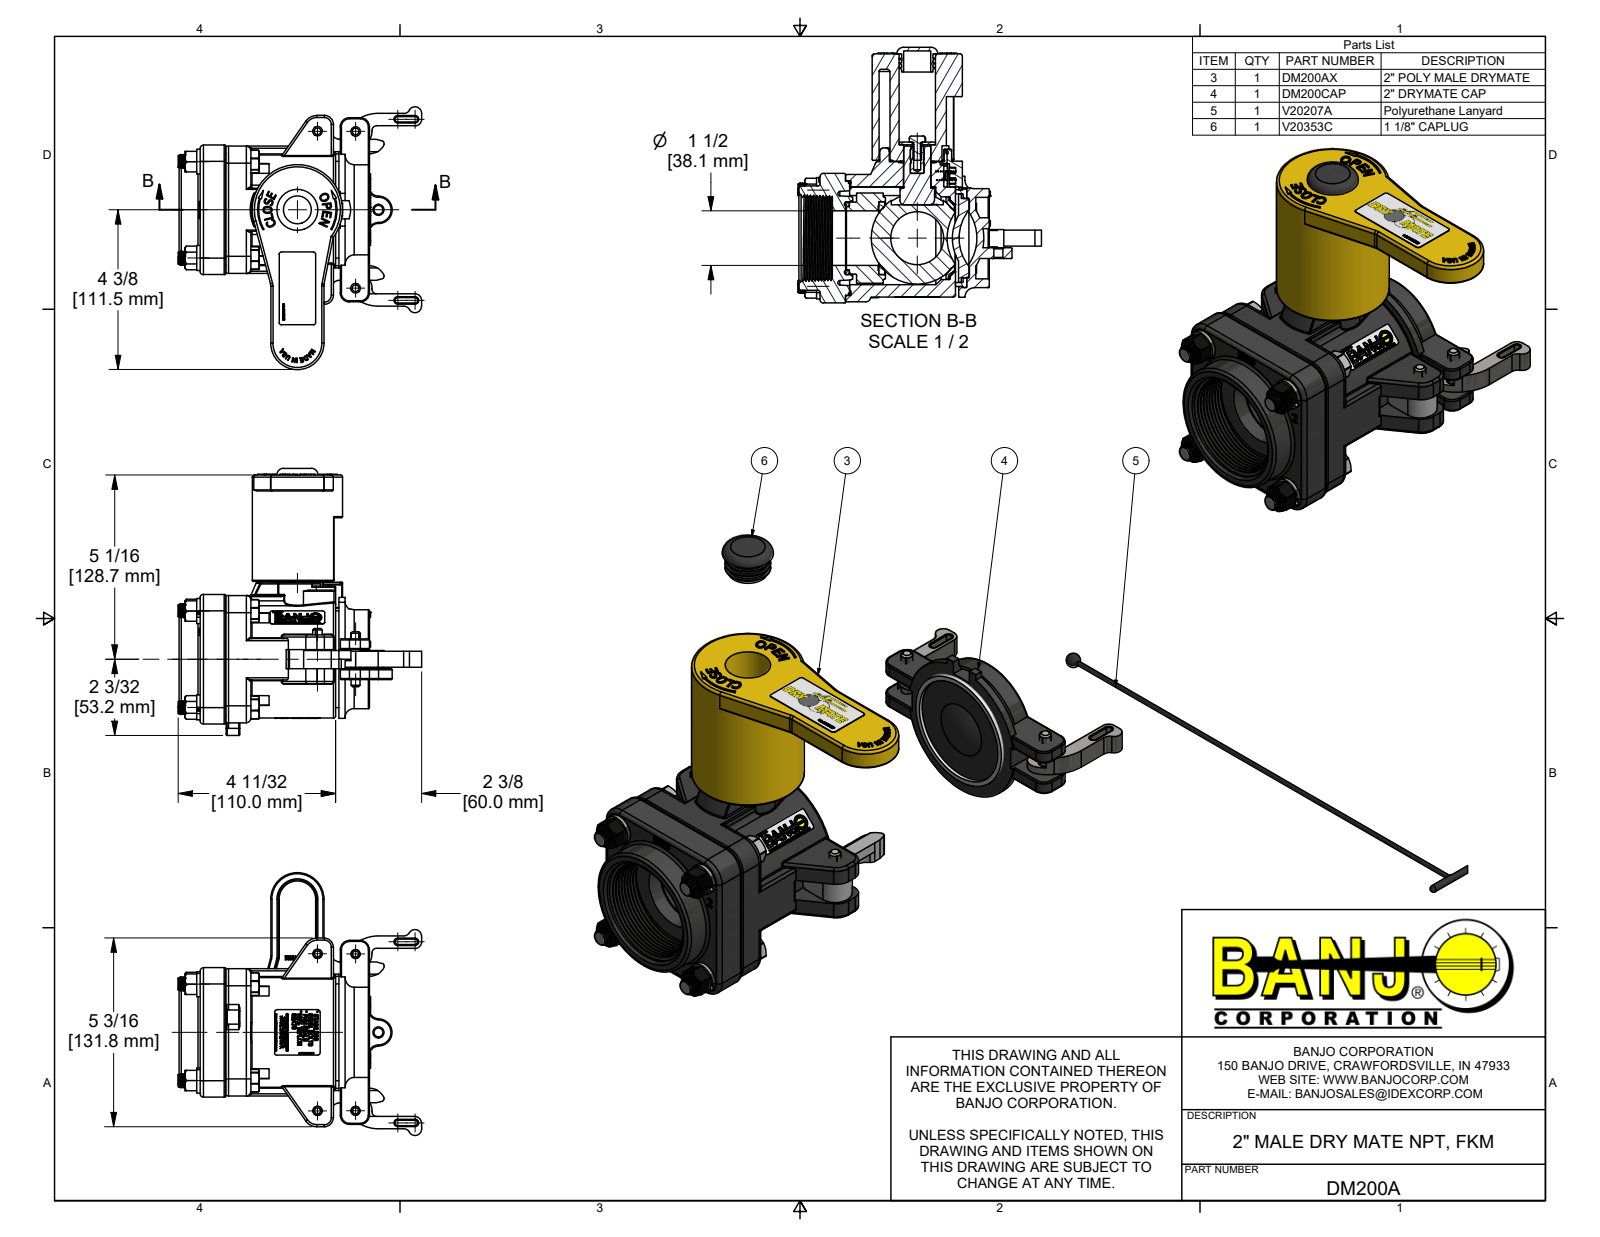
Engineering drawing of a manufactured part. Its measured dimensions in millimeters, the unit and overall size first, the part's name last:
Units: millimetres
Overall size (bounding box): 186.4 × 183.4 × 170.1
Round holes (diameter × count): ⌀6.4 ×5, ⌀9.5 ×5, ⌀6.5 ×4, ⌀7.8 ×4, ⌀9.8 ×4, ⌀10.3 ×4, ⌀10.7 ×4, ⌀3.2 ×3, ⌀5 ×1, ⌀5.1 ×1, ⌀5.8 ×1, ⌀7.1 ×1
Round bosses / shafts (diameter × count): ⌀8.2 ×60, ⌀17.4 ×4, ⌀9.5 ×4, ⌀6.6 ×4, ⌀6.3 ×4, ⌀7.1 ×3, ⌀63 ×2, ⌀82.6 ×1
Partial cylindrical surfaces — rounded edges, fillets, slot ends (radius × count): R0.8 ×104, R1.5 ×52, R0.5 ×20, R0.3 ×12, R3.2 ×10, R6.4 ×10, R2.3 ×8, R4.1 ×8
Main face-to-face distances: 7.6, 94.6, 7.5, 0.8, 89.7, 6.4, 20.9, 20.9, 17.8, 76.8
Hole centre spacings: 67.4, 47.5, 47.8, 67.3, 67.5, 95.3, 24.1, 25
Volume: 816 400 mm³ · Surface area: 277 200 mm²
Bodies: 45 solids, 6014 faces (2863 planar, 888 cylindrical, 2263 other)
Part name (STEP PRODUCT): DM200A; DM200AX; DM20254; DM20254MY (+8 more)
STEP written by: Autodesk Inventor 2022 (AUTOMOTIVE_DESIGN)
